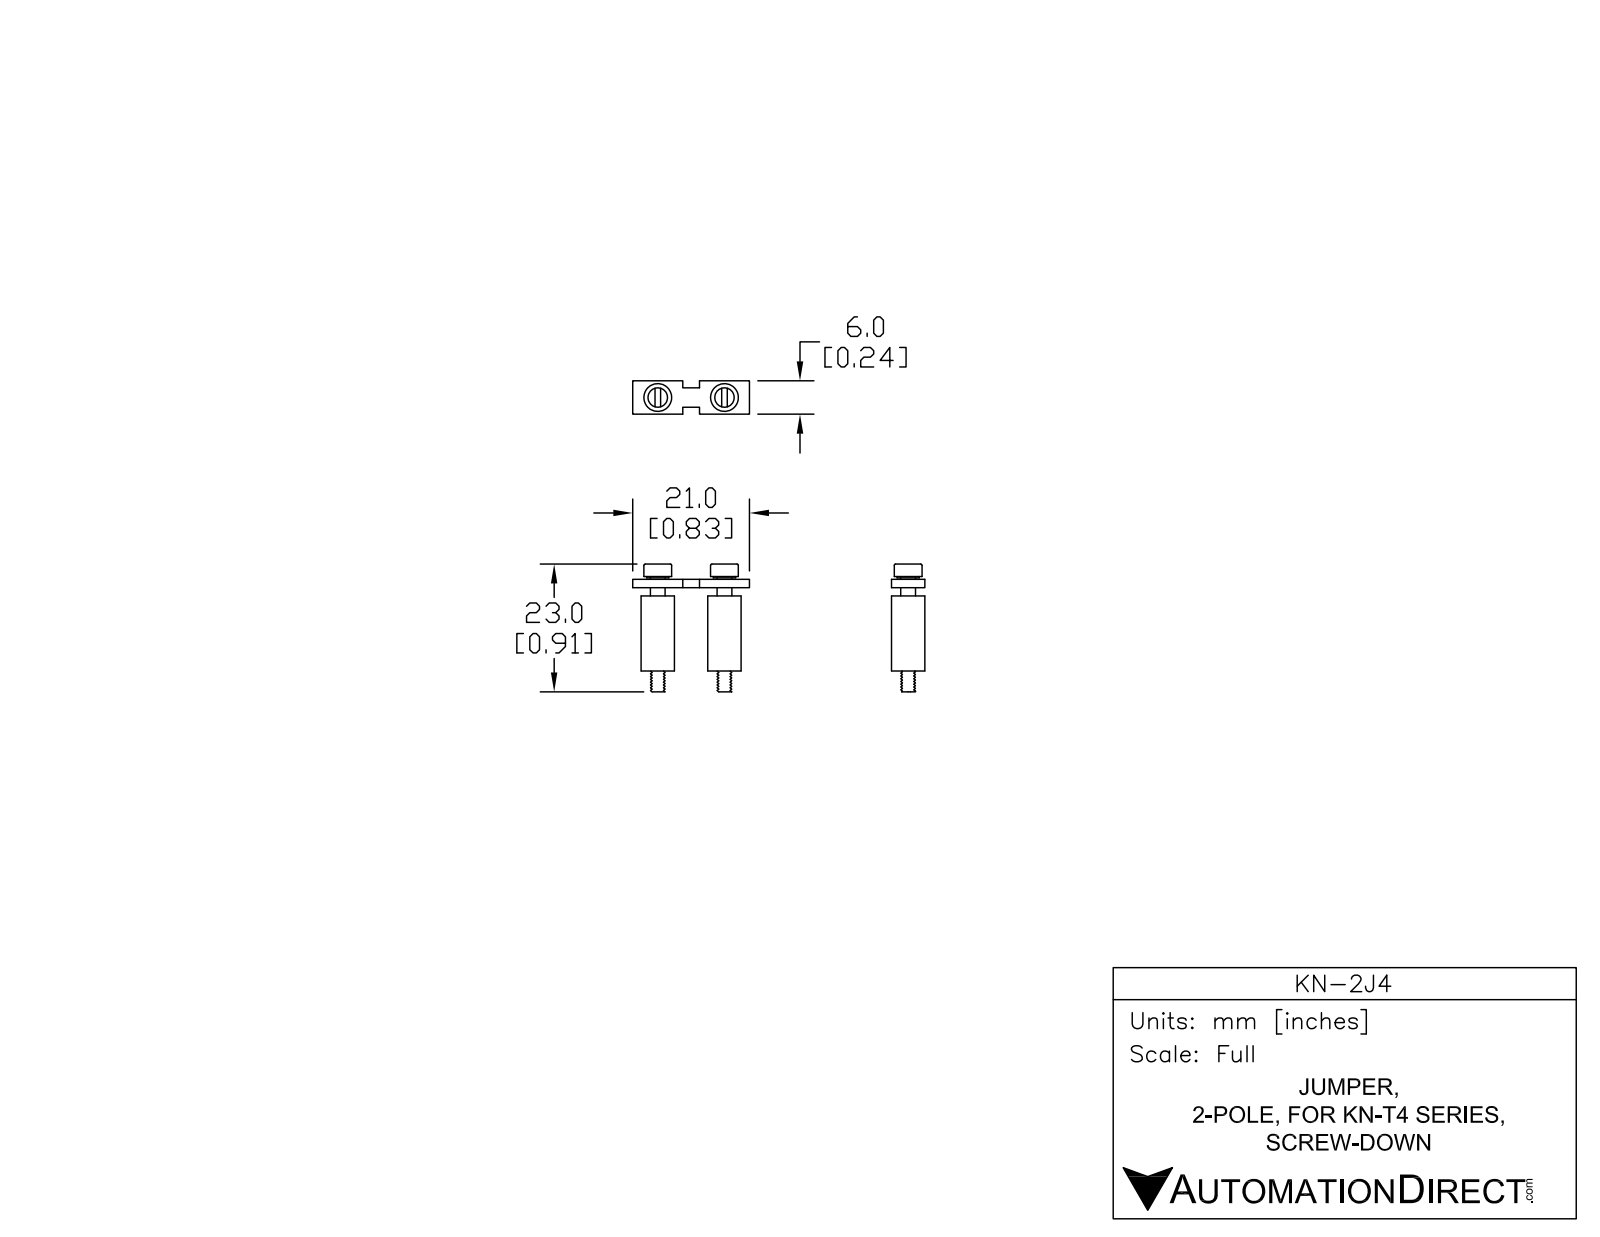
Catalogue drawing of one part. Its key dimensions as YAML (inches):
part_name: "KN-2J4"
step_written_by: "SolidWorks 2014 (AUTOMOTIVE_DESIGN)"
units: inches
bodies: {solids: 7, faces: 82, planar: 40, cylindrical: 30, other: 12}
overall_size: [0.906, 0.827, 0.236]
volume: 0.058
surface_area: 2.889
round_holes:
  - {diameter: 0.124, count: 2}
  - {diameter: 0.138, count: 2}
round_bosses_or_shafts:
  - {diameter: 0.236, count: 2}
  - {diameter: 0.197, count: 2}
  - {diameter: 0.157, count: 2}
  - {diameter: 0.104, count: 2}
face_to_face_distances: [0.059, 0.118, 0.65, 0.531, 0.591, 0.079, 0.02, 0.069, 0.089, 0.669]
hole_center_spacings: [0.472]
